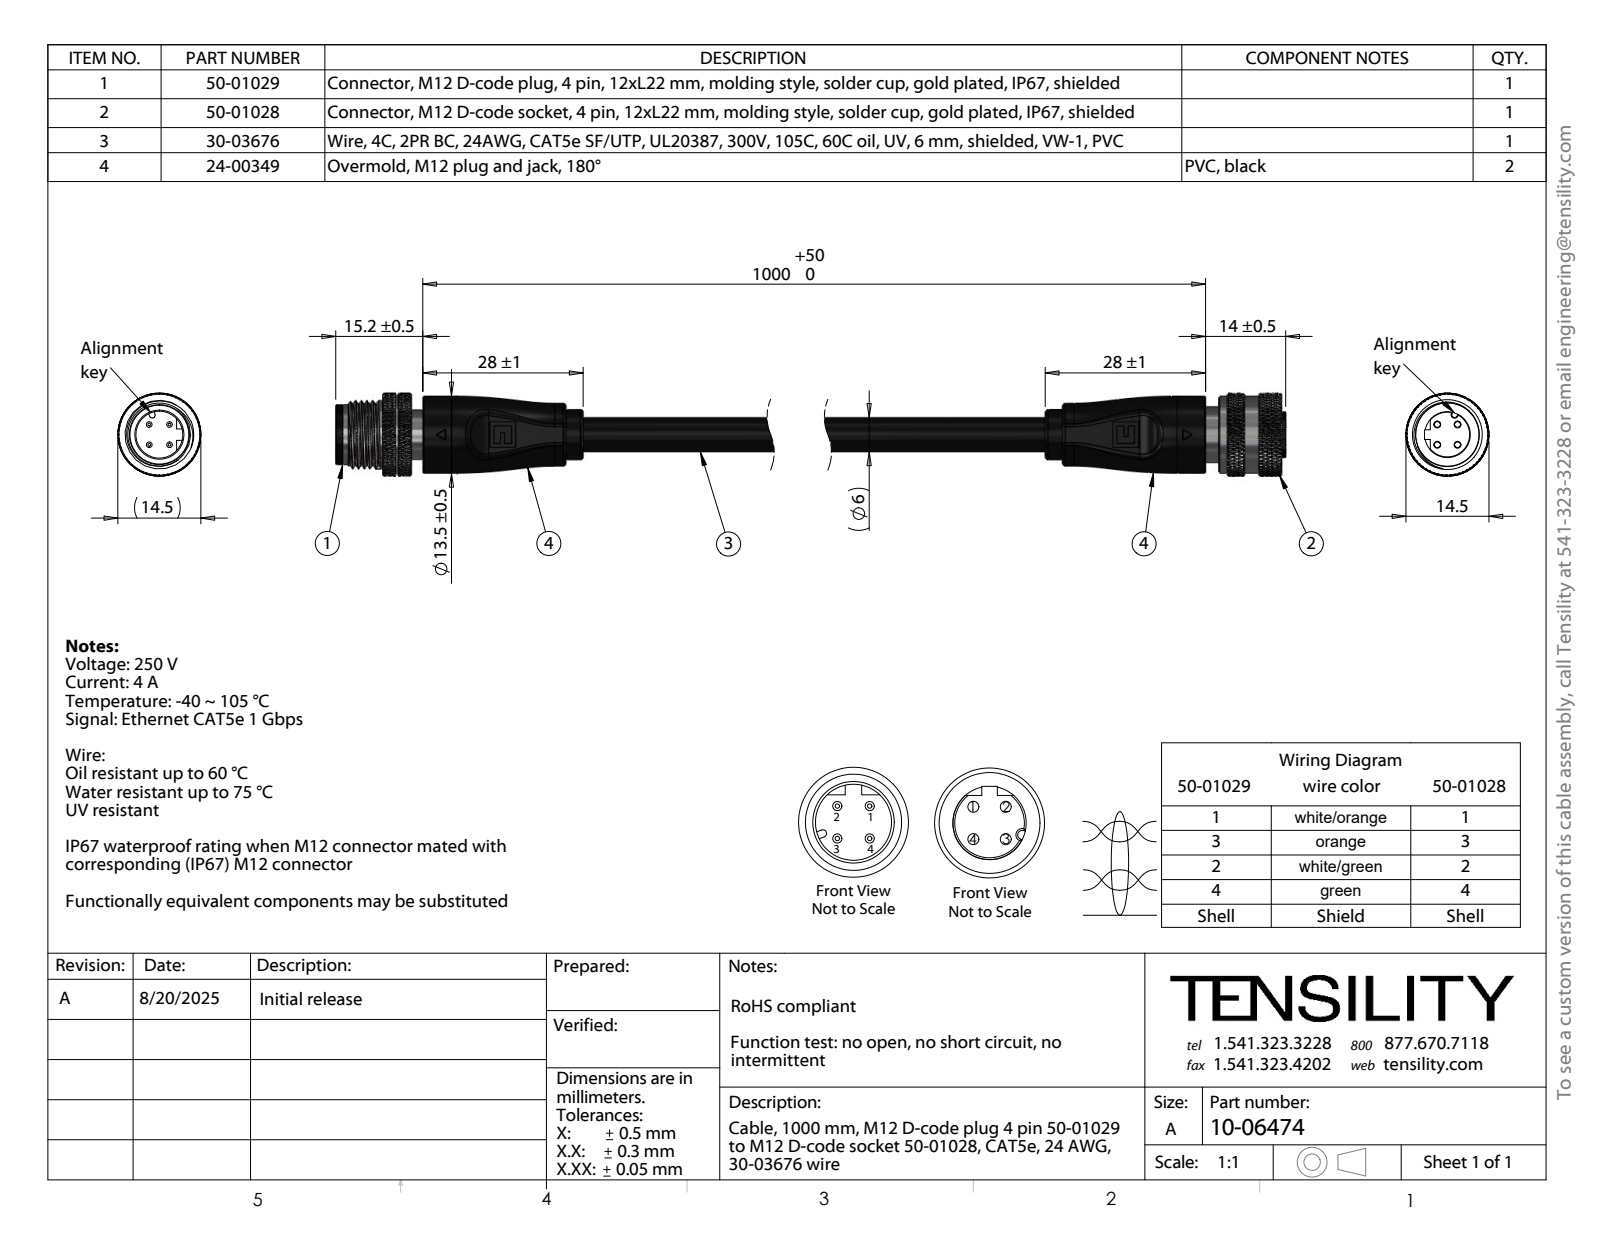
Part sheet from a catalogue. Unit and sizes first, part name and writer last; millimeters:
Units: millimetres
Overall size (bounding box): 235.2 × 14.5 × 14.5
Round holes (diameter × count): ⌀0.2 ×28, ⌀1 ×4, ⌀1.05 ×4, ⌀1.1 ×4, ⌀1.2 ×4, ⌀3.16 ×1, ⌀3.21 ×1, ⌀3.56 ×1, ⌀8.2 ×1, ⌀9.5 ×1, ⌀10 ×1, ⌀11.2 ×1
Round bosses / shafts (diameter × count): ⌀1.6 ×4, ⌀1.5 ×4, ⌀1.4 ×4, ⌀14.5 ×1, ⌀13.9 ×1, ⌀13.5 ×1, ⌀12 ×1, ⌀11 ×1
Partial cylindrical surfaces — rounded edges, fillets, slot ends (radius × count): R0.1 ×10, R0.4 ×6, R0.5 ×4, R1.5 ×2, R1.96 ×2, R5 ×2, R5.58 ×1, R6.75 ×1
Main face-to-face distances: 206, 7, 28, 178, 2, 208, 3.8, 211.8, 208.3, 5.8
Hole centre spacings: 1.91, 0.36, 2.09, 1.06, 0.89, 1.08, 1.24, 1.8
Volume: 13 734 mm³ · Surface area: 30 639 mm²
Bodies: 53 solids, 5792 faces (362 planar, 1477 cylindrical, 3953 other)
Part name (STEP PRODUCT): 24-00349_Mexico; 50-01029_默认; 50-01028-04_默认; 50-01028-02_默认 (+8 more)
STEP written by: SolidWorks 2025 (CONFIG_CONTROL_DESIGN)
